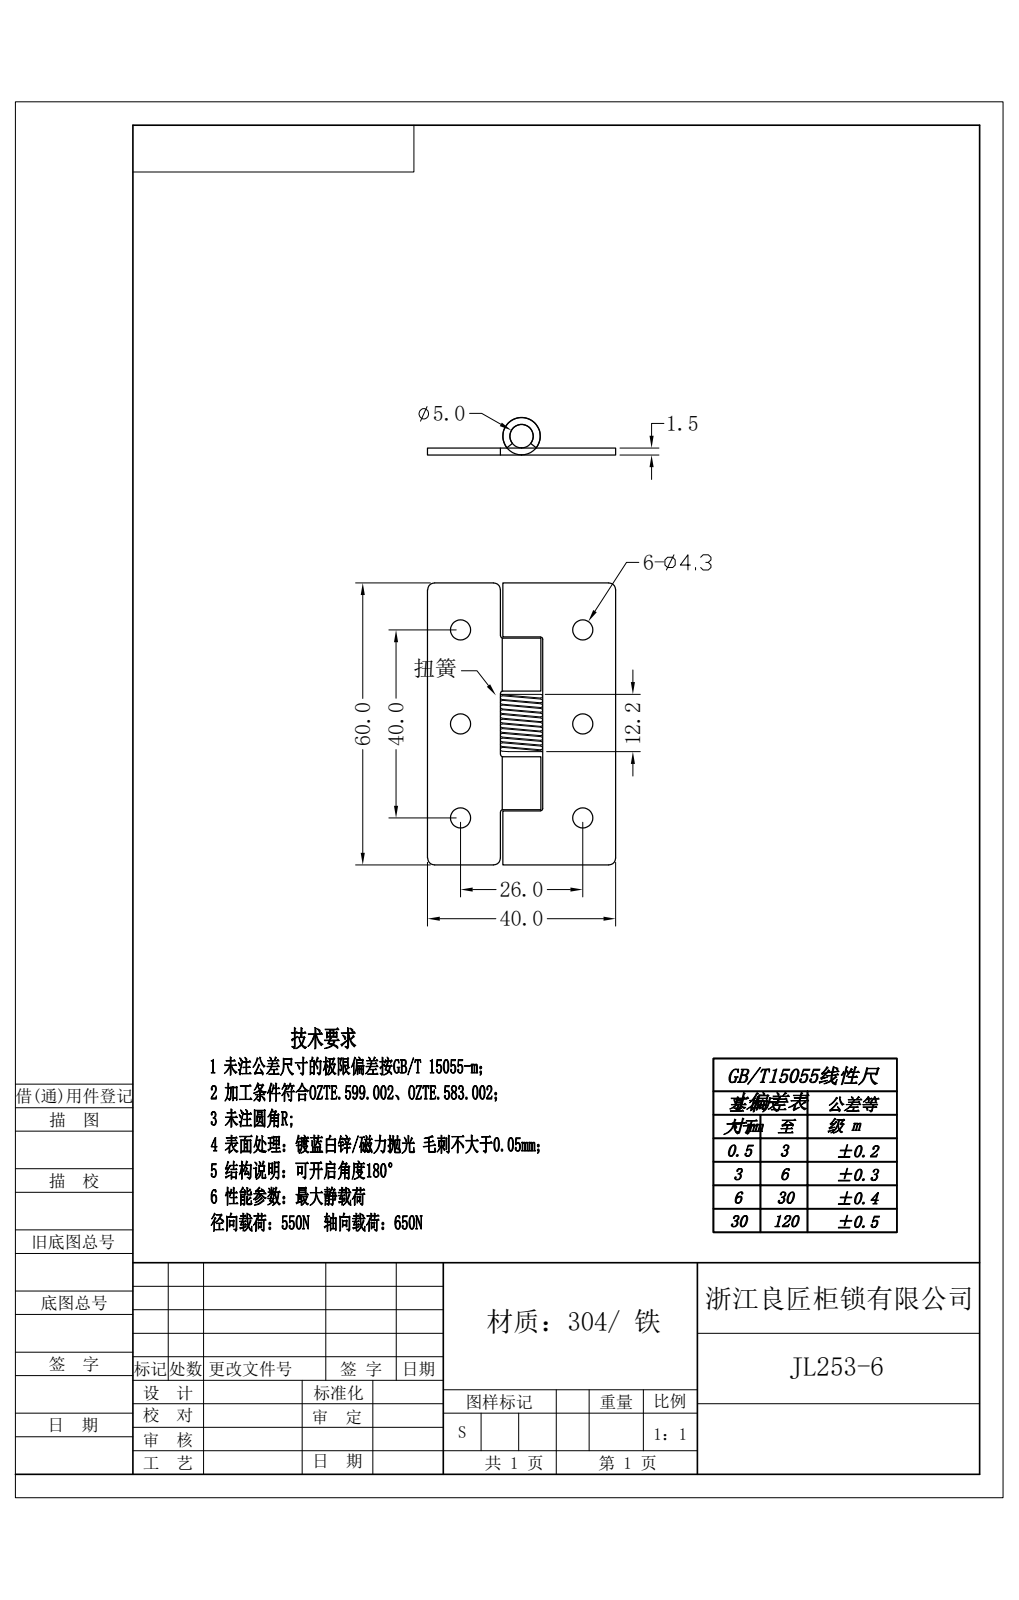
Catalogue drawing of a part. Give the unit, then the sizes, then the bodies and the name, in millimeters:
Units: millimetres
Overall size (bounding box): 154.31 × 60 × 34.92
Round holes (diameter × count): ⌀4.3 ×12, ⌀5 ×2
Round bosses / shafts (diameter × count): ⌀0.9 ×6, ⌀1 ×3, ⌀8 ×2, ⌀4.7 ×1
Partial cylindrical surfaces — rounded edges, fillets, slot ends (radius × count): R0.5 ×12, R1.5 ×12
Main face-to-face distances: 1.5, 1.48, 11.5, 37, 60, 48.5, 23, 25.5, 11.75, 48.25
Hole centre spacings: 20, 40, 133.81
Volume: 10 009 mm³ · Surface area: 16 474 mm²
Bodies: 7 solids, 152 faces (54 planar, 84 cylindrical, 14 other)
STEP written by: Rhino 8.5 (CONFIG_CONTROL_DESIGN)
